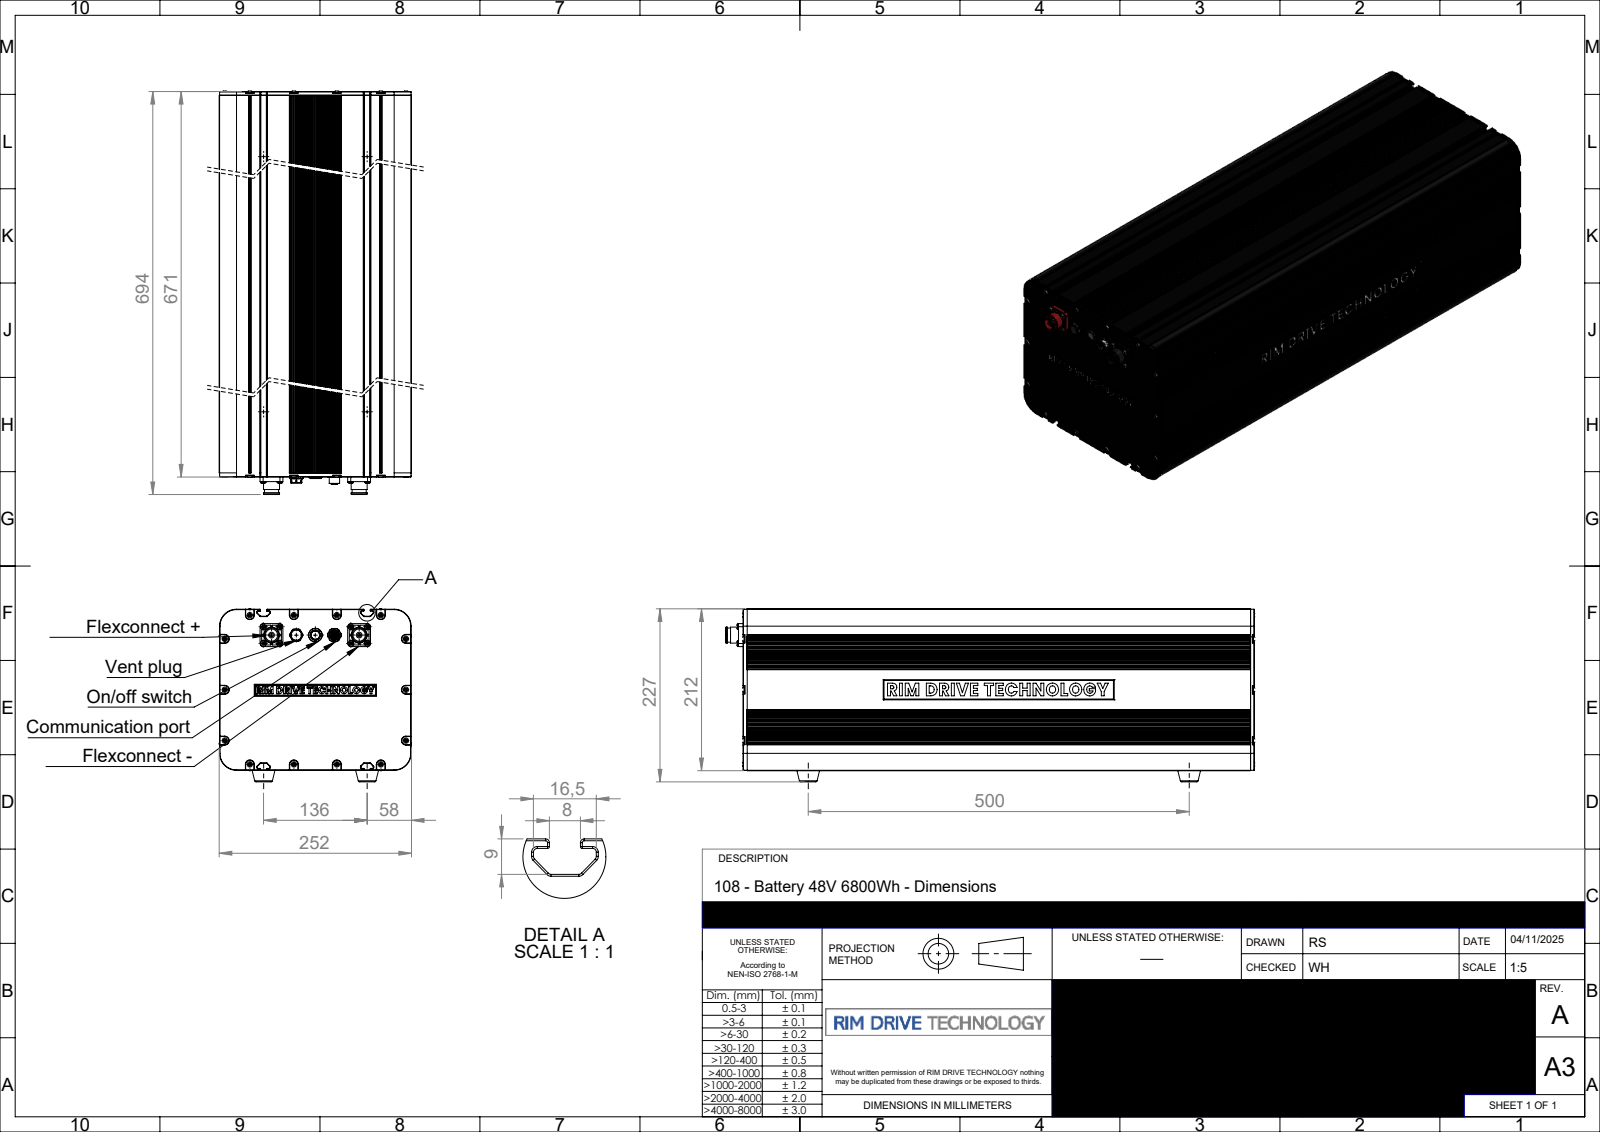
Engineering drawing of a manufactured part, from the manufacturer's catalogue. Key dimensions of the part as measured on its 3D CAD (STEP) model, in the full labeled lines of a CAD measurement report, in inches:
Part name (STEP PRODUCT): P-108-201-rev-A-48V 6800Wh
STEP written by: SolidWorks 2024 (AUTOMOTIVE_DESIGN)
Units: inches
Bodies: 1 solid, 4104 faces (1829 planar, 1340 cylindrical, 935 other)
Overall size (bounding box): 27.346 × 9.935 × 8.941
Volume: 2 134 in³ · Surface area: 1 371 in²
Round holes (diameter × count): ⌀0.043 ×4, ⌀0.417 ×4, ⌀0.079 ×3, ⌀0.63 ×2, ⌀0.287 ×1, ⌀0.452 ×1, ⌀0.465 ×1
Round bosses / shafts (diameter × count): ⌀0.276 ×22, ⌀0.374 ×4, ⌀0.827 ×2, ⌀0.732 ×2, ⌀0.295 ×2, ⌀0.701 ×1, ⌀0.571 ×1, ⌀0.534 ×1
Partial cylindrical surfaces — rounded edges, fillets, slot ends (radius × count): R0.02 ×292, R0.013 ×84, R0.023 ×84, R0.011 ×48, R0.027 ×48, R0.039 ×32, R0.018 ×24, R0.031 ×24
Main face-to-face distances: 8.323, 9.896, 0.02, 9.876, 26.417, 0.098, 8.224, 0.197, 9.857, 8.126
Hole centre spacings: 0.092, 0.13, 0.184, 0.922, 0.984, 1.051, 1.216, 1.28
